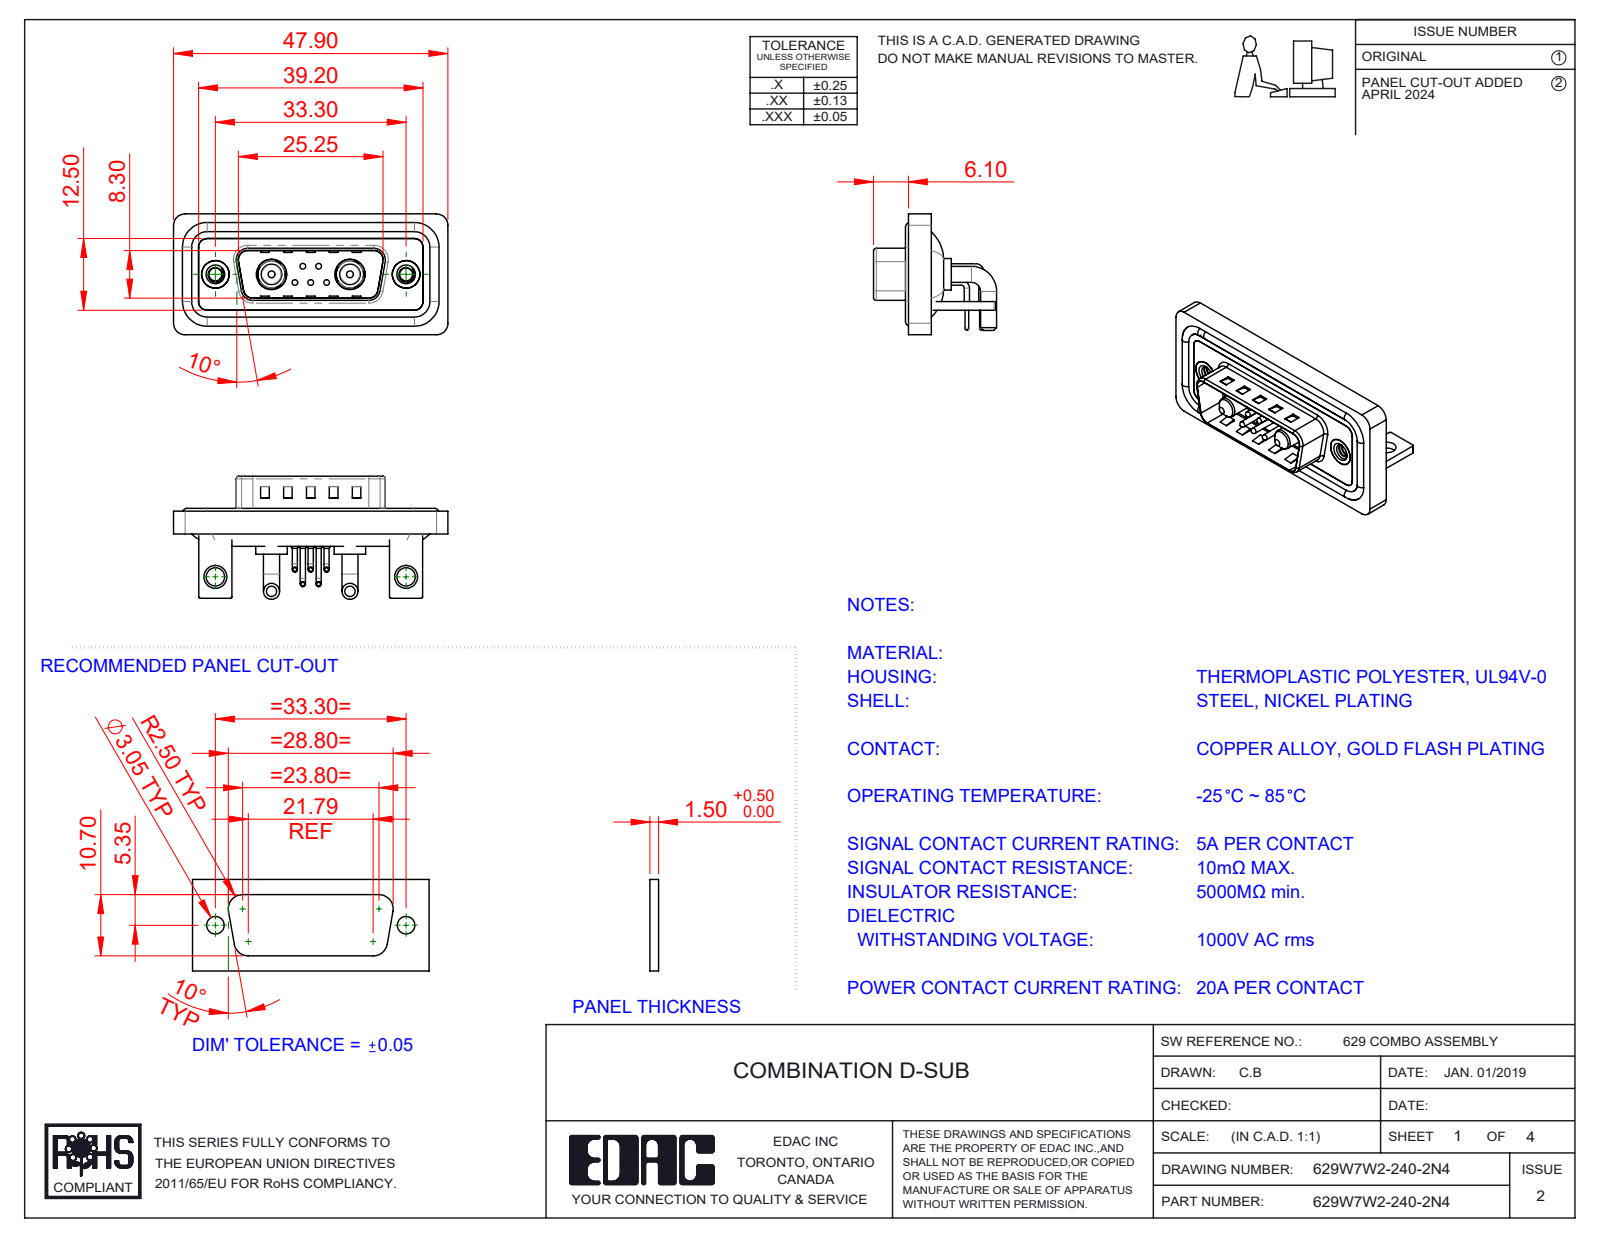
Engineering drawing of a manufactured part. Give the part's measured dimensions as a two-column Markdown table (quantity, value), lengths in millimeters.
| quantity | value |
| --- | --- |
| part name | Power Pin_20A RA; 629Combo Shell Front_15 Contacts; 629Combo Contact Row 2; 629Combo Housing_7W2 (+6 more) |
| STEP written by | SolidWorks 2023 (CONFIG_CONTROL_DESIGN) |
| units | millimeters |
| bodies | 18 solids, 1123 faces (537 planar, 424 cylindrical, 162 other) |
| overall size | 47.9 × 21.5 × 21.1 |
| volume | 5 958 mm³ |
| surface area | 9 727 mm² |
| round holes (diameter × count) | 0.75 × 5, 1.6 × 5, 2 × 5, 2.26 × 2, 3.2 × 2, 4 × 2, 4.8 × 2, 4.85 × 2, 5 × 2, 5.3 × 2 |
| round bosses / shafts (diameter × count) | 0.9 × 10, 1.5 × 5, 1 × 5, 0.65 × 5, 2.8 × 4, 1.6 × 4, 5.5 × 2, 5.2 × 2 |
| partial cylindrical surfaces (radius × count) | 2 × 21, 1.5 × 18, 0.25 × 16, 0.5 × 9, 1.6 × 8, 1.01 × 5, 0.6 × 4, 0.65 × 4 |
| main face-to-face distances | 0.4, 1.5, 0.8, 2.9, 2.1, 1.1, 1.6, 1.2, 3.7, 4.5 |
| hole center spacings | 3.16, 2.77, 9.8, 23.5, 33.3, 4.31, 4.33, 5.03 |
